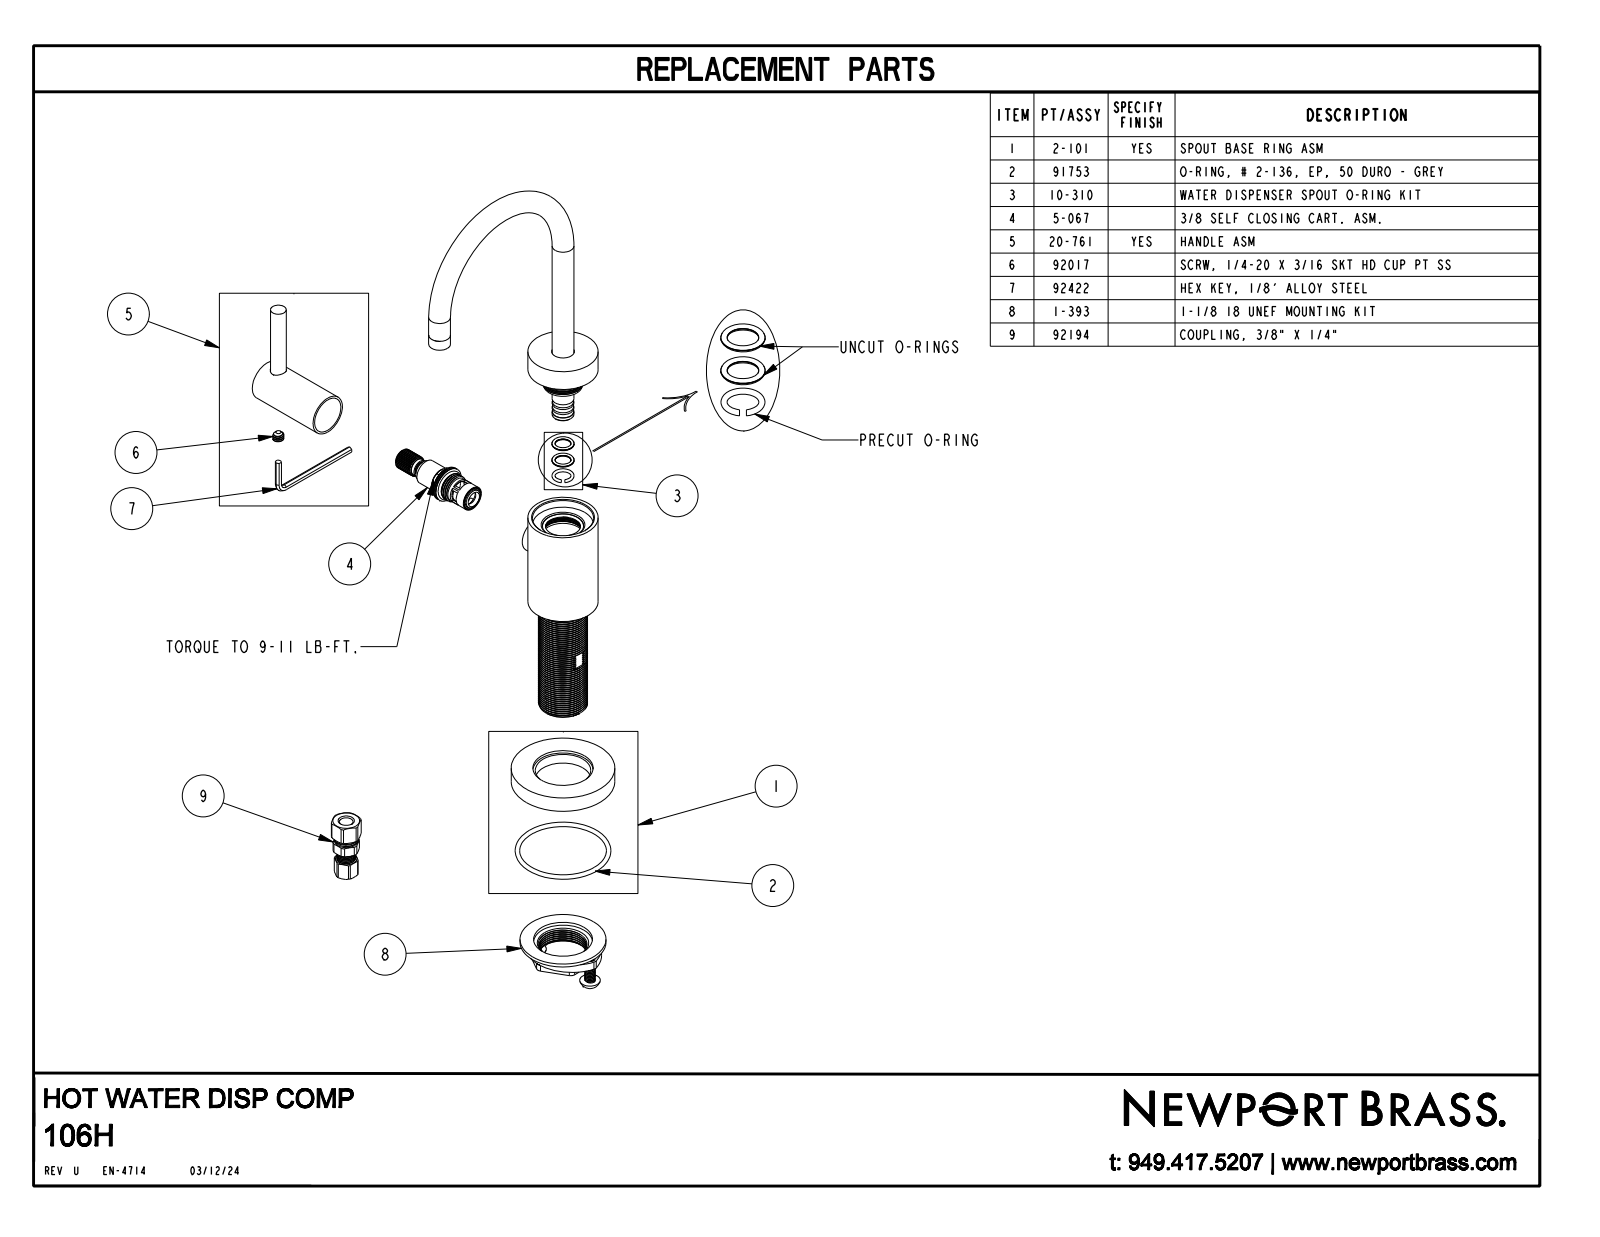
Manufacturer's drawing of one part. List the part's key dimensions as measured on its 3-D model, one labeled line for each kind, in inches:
Part name (STEP PRODUCT): 106H
STEP written by: CREO PARAMETRIC BY PTC INC, 2018400 (CONFIG_CONTROL_DESIGN)
Units: inches
Bodies: 1 solid, 23 faces (7 planar, 14 cylindrical, 2 other)
Overall size (bounding box): 9.275 × 5.437 × 3.751
Volume: 10.99 in³ · Surface area: 51.17 in²
Round holes (diameter × count): ⌀1 ×1
Round bosses / shafts (diameter × count): ⌀0.5 ×2, ⌀2.375 ×1, ⌀1.61 ×1, ⌀0.95 ×1, ⌀0.36 ×1
Main face-to-face distances: 0.375, 3.225, 2.85, 6.525, 6.15, 3.3, 4.067, 3.692, 0.842, 2.458
